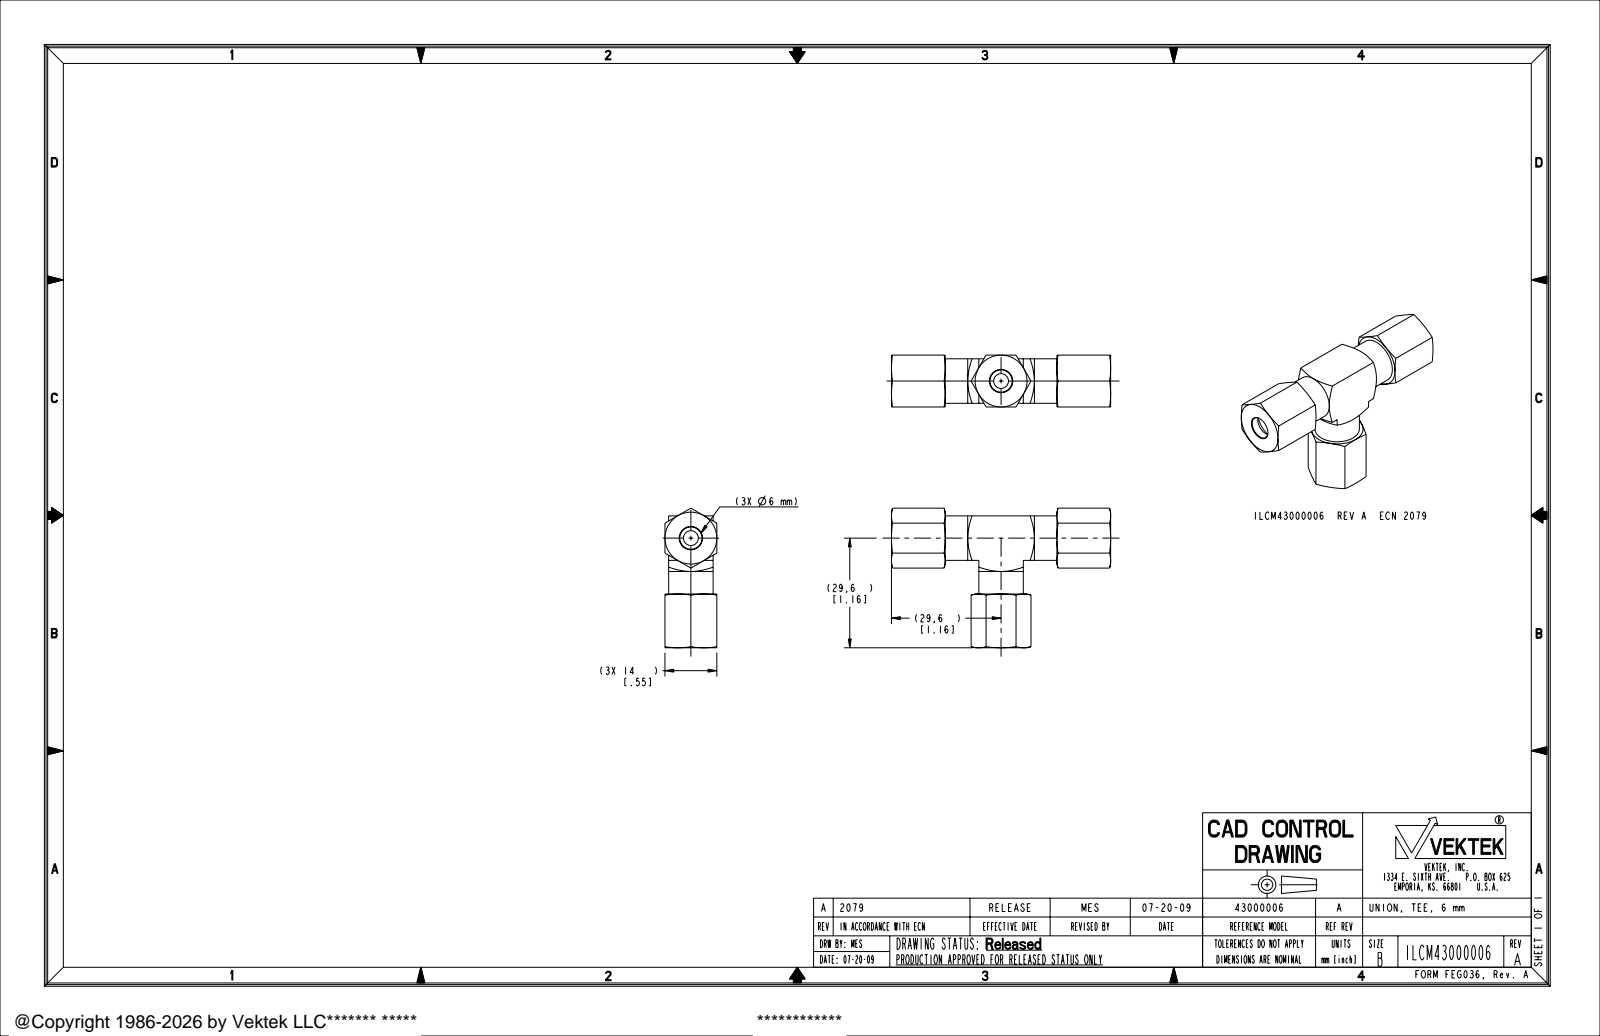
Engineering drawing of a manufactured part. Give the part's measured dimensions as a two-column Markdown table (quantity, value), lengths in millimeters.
| quantity | value |
| --- | --- |
| part name | ILCM43000006 |
| STEP written by | PRO/ENGINEER BY PARAMETRIC TECHNOLOGY CORPORATION, 2007460 (AUTOMOTIVE_DESIGN_CC2) |
| units | millimeters |
| bodies | 1 solid, 137 faces (37 planar, 28 cylindrical, 72 other) |
| overall size | 59.2 × 37.7 × 14 |
| volume | 9 140 mm³ |
| surface area | 6 269 mm² |
| round holes (diameter × count) | 4 × 2, 6 × 2, 10.4 × 2 |
| round bosses / shafts (diameter × count) | 12 × 2 |
| main face-to-face distances | 14, 13, 1, 12, 35.6, 23.6, 59.1, 14.5, 9.1, 21.1 |
